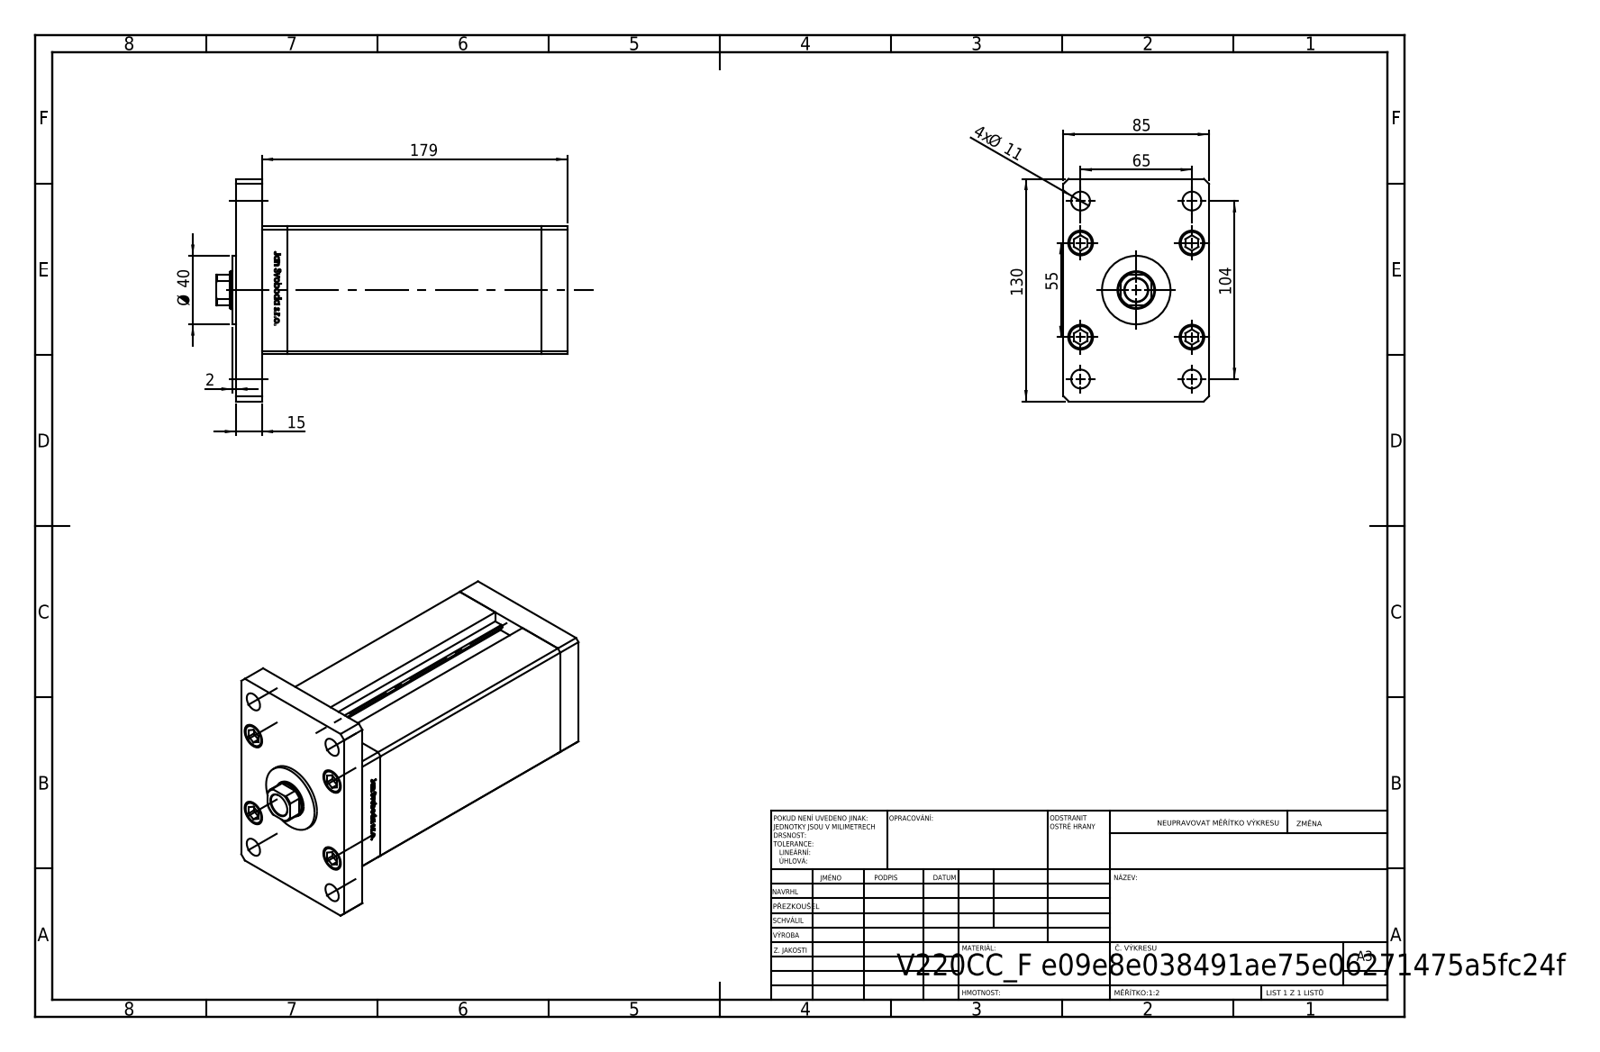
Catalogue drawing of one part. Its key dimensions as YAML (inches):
part_name: "ALLEN BOLT; V220C BACK_F; V220C_VC_F; V220C_FRONT_F (+2 more)"
step_written_by: "SolidWorks 2019 (CONFIG_CONTROL_DESIGN)"
units: inches
bodies: {solids: 19, faces: 1310, planar: 517, cylindrical: 187, other: 606}
overall_size: [8.071, 5.118, 3.346]
volume: 71.09
surface_area: 308.3
round_holes:
  - {diameter: 0.433, count: 9}
  - {diameter: 0.61, count: 5}
  - {diameter: 0.394, count: 4}
  - {diameter: 0.571, count: 4}
  - {diameter: 0.079, count: 2}
  - {diameter: 0.518, count: 2}
  - {diameter: 0.531, count: 1}
  - {diameter: 0.866, count: 1}
  - {diameter: 0.925, count: 1}
round_bosses_or_shafts:
  - {diameter: 0.315, count: 9}
  - {diameter: 0.571, count: 5}
  - {diameter: 1.575, count: 1}
partial_cylinders:
  - {radius: 0.037, count: 2}
  - {radius: 0.413, count: 1}
face_to_face_distances: [0.591, 3.346, 6.437, 7.028, 2.953, 1.181, 5.846, 7.618, 0.413, 1.083]
hole_center_spacings: [1.102, 0.965, 1.676, 2.414, 2.559, 2.735, 3.13, 4.043]
